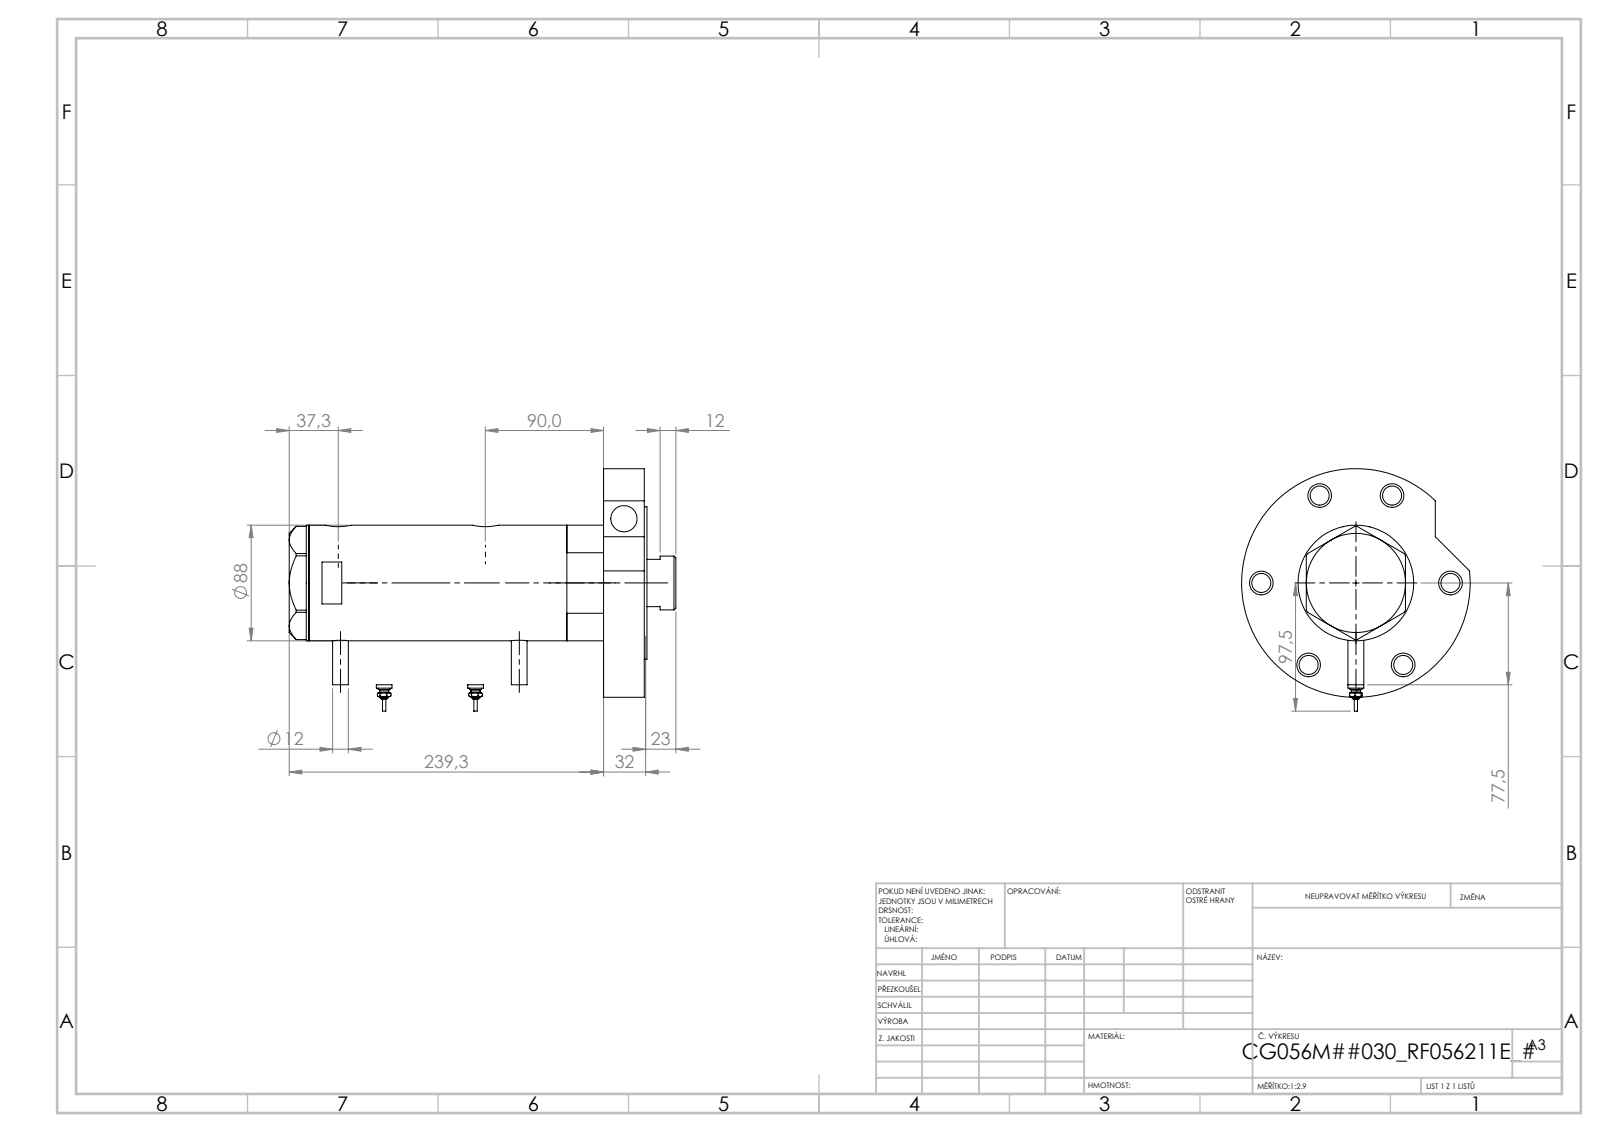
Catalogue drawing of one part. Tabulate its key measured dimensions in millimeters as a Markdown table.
| quantity | value |
| --- | --- |
| part name | V270CG_VC; V270CG_SWITCH; V270CG_FRONT; V270CG_BACK (+2 more) |
| STEP written by | SolidWorks 2019 (CONFIG_CONTROL_DESIGN) |
| units | millimeters |
| bodies | 7 solids, 276 faces (92 planar, 110 cylindrical, 74 other) |
| overall size | 254.47 × 174 × 174 |
| volume | 1 834 000 mm³ |
| surface area | 277 405 mm² |
| round holes (diameter × count) | 14.5 × 7, 18 × 6, 20 × 3, 5 × 2, 12.5 × 2, 13.16 × 2, 42 × 1, 43.5 × 1, 56 × 1, 60 × 1, 75 × 1, 80 × 1 |
| round bosses / shafts (diameter × count) | 12 × 2, 9 × 2, 7 × 2, 4.34 × 2, 2.4 × 2, 174 × 1, 116 × 1, 88 × 1 |
| main face-to-face distances | 31, 2, 214.9, 181.9, 212.9, 33, 104.4, 77.5, 108.5, 110.5 |
| hole center spacings | 72, 80, 119.73, 124.71, 129.15, 143.69, 1.7, 25.8 |
